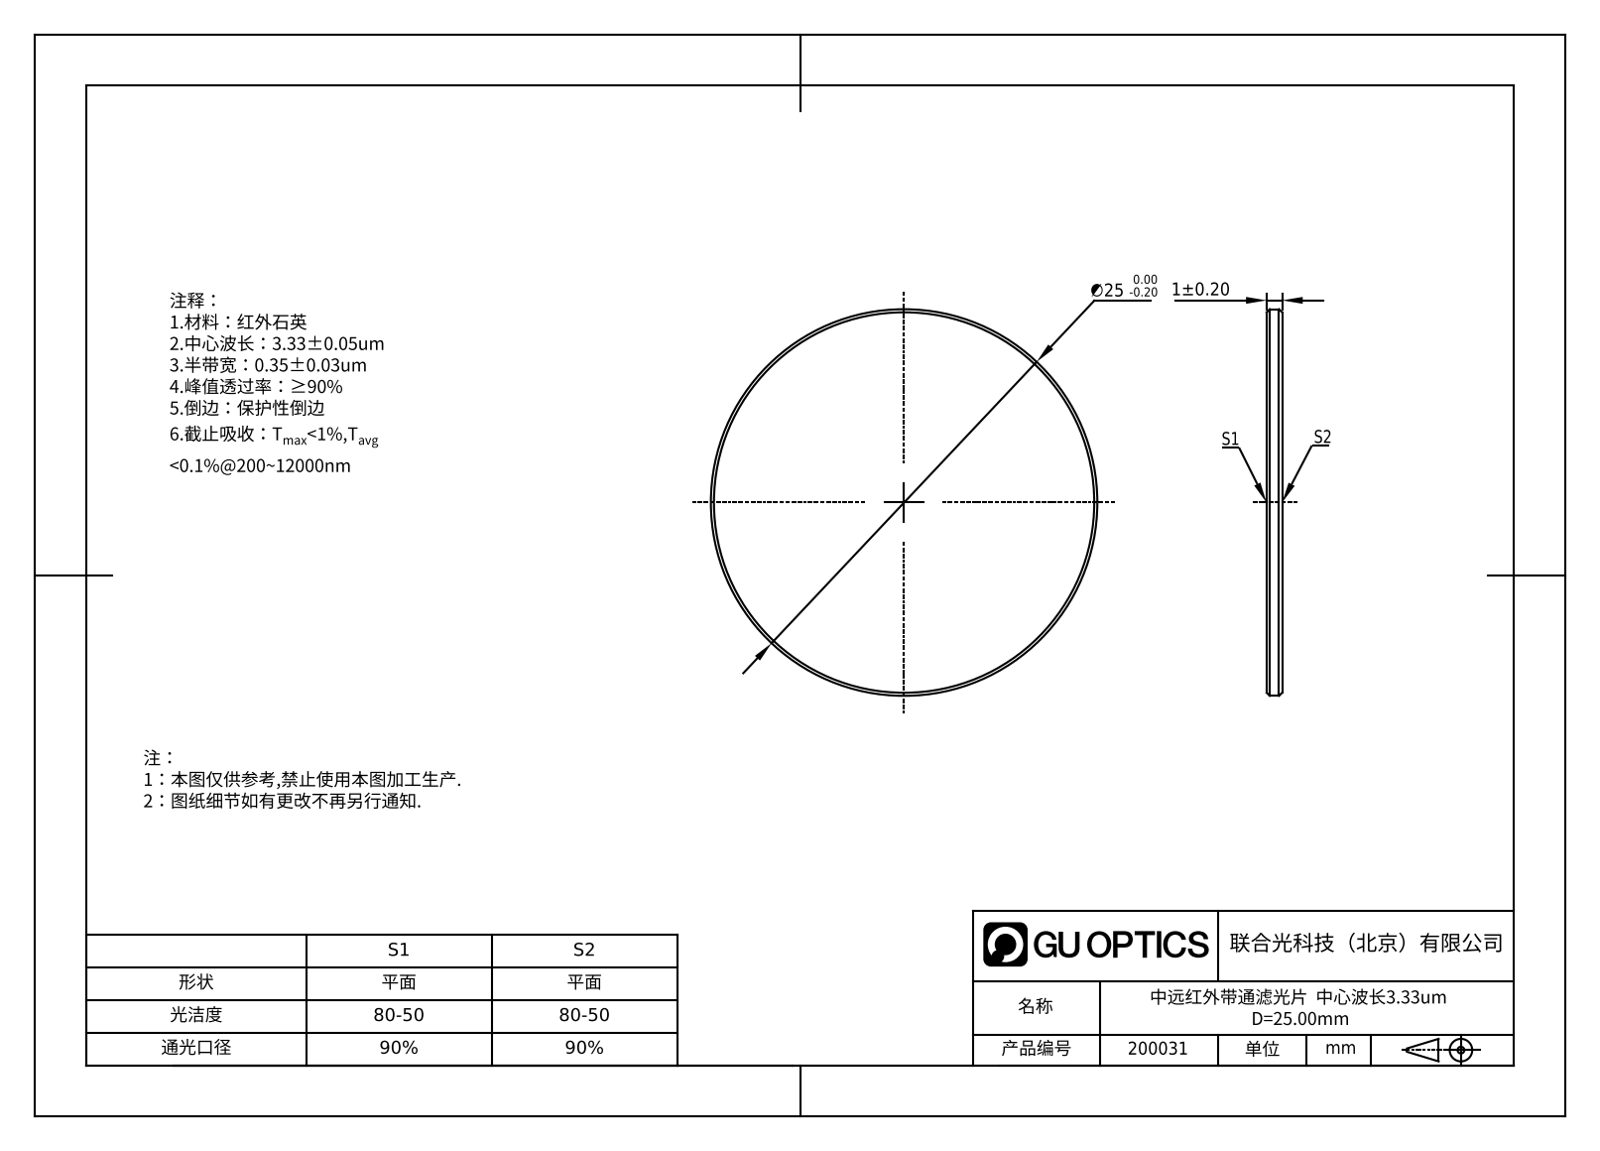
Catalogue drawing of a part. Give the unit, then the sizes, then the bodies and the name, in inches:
Units: inches
Overall size (bounding box): 0.984 × 0.984 × 0.039
Round bosses / shafts (diameter × count): ⌀0.984 ×1
Main face-to-face distances: 0.039
Volume: 0.03 in³ · Surface area: 1.615 in²
Bodies: 1 solid, 8 faces (2 planar, 2 cylindrical, 4 other)
Part name (STEP PRODUCT): GNIF-350-3330-D25
STEP written by: SolidWorks 2022 (AUTOMOTIVE_DESIGN)
